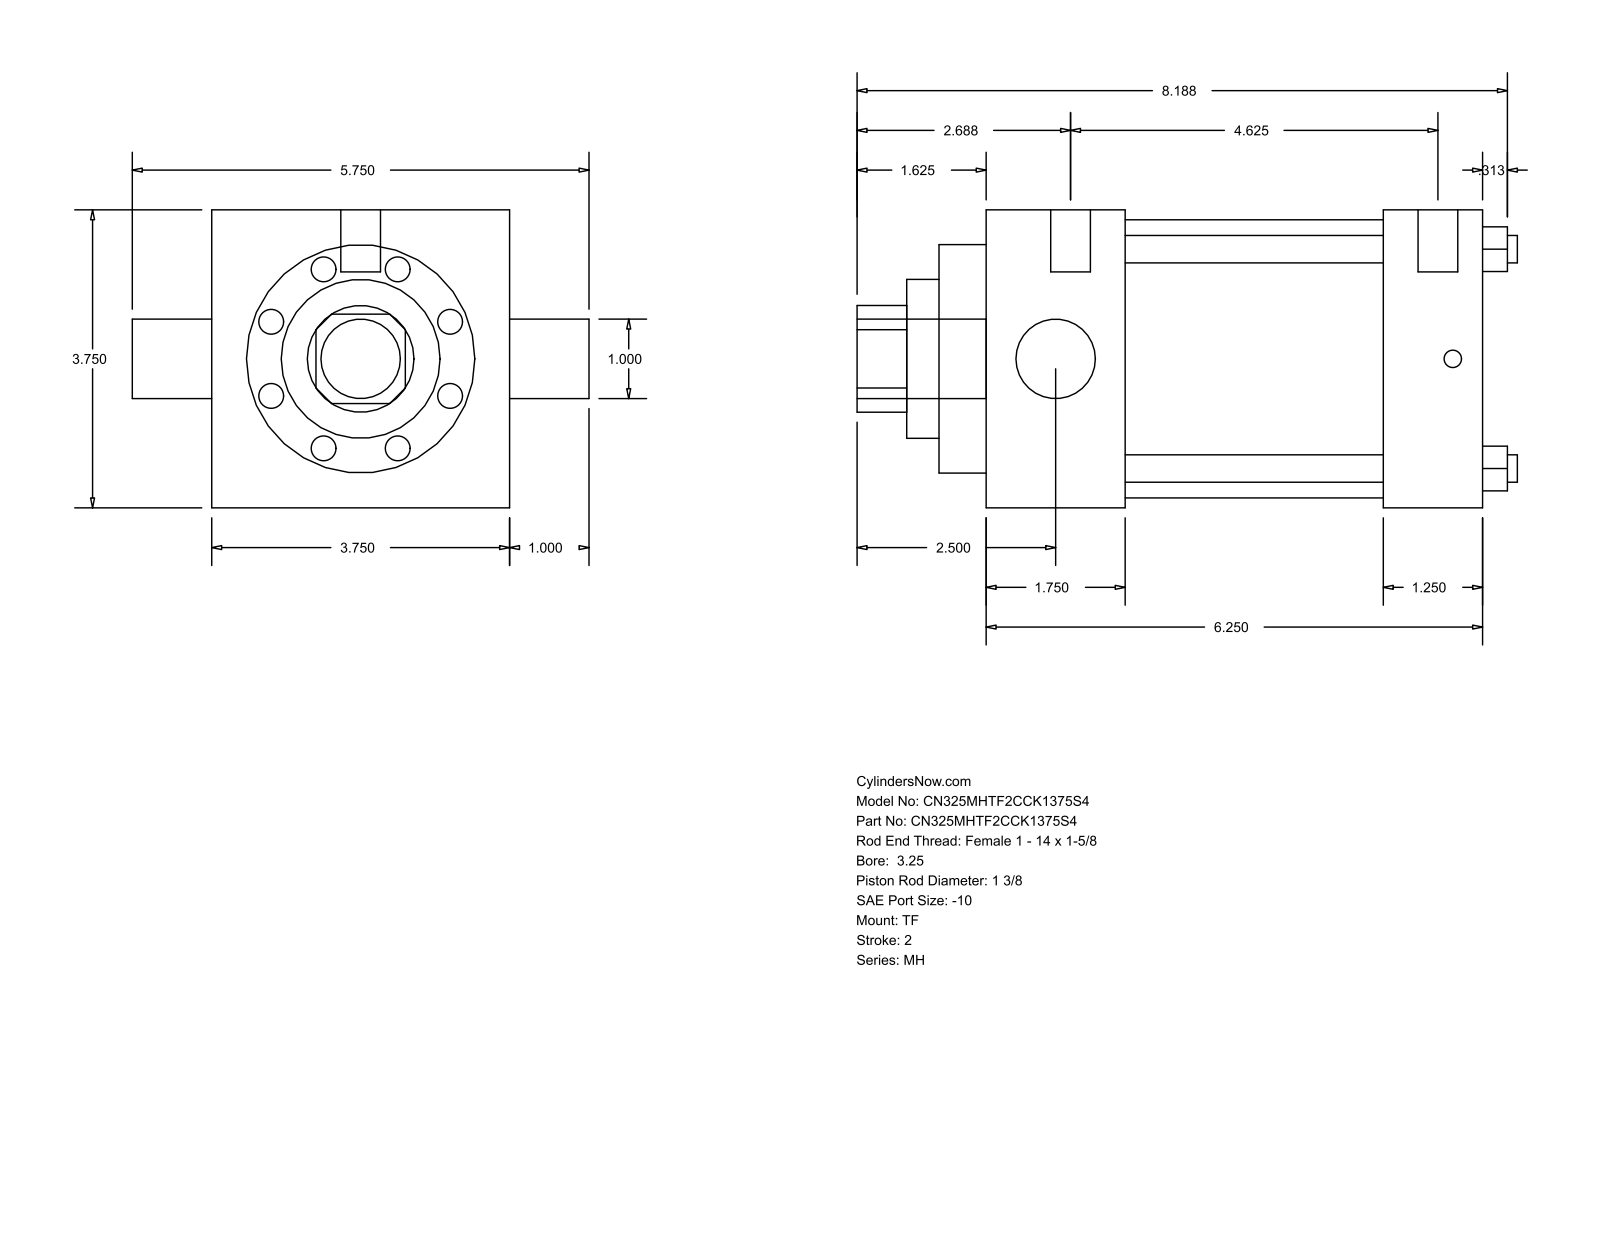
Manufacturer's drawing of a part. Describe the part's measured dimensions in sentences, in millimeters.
The part is named "MH_TF__0325_1.375". Its 3-D file was written by "GSSL Pune (CONFIG_CONTROL_DESIGN)". It is 0 solids with 86 faces: 61 planar, 25 cylindrical and 0 other. Overall it measures 211.14 by 146.05 by 95.25 millimeters. Round holes: 4 of diameter 8.76, 1 of diameter 25.4, 1 of diameter 34.92, 1 of diameter 50.8, 1 of diameter 73.03, 1 of diameter 88.9. Round bosses or shafts: 3 of diameter 5.56, 2 of diameter 12.7, 1 of diameter 25.4. Partial cylindrical surfaces (rounded edges, fillets, slot ends): 1 of radius 17.06. The main face-to-face distances are 95.24, 158.76, 44.45, 127.01, 82.56, 114.31, 31.75, 15.08, 59.53, 142.09. The hole center spacings are 49.57, 70.1, 99.14.
